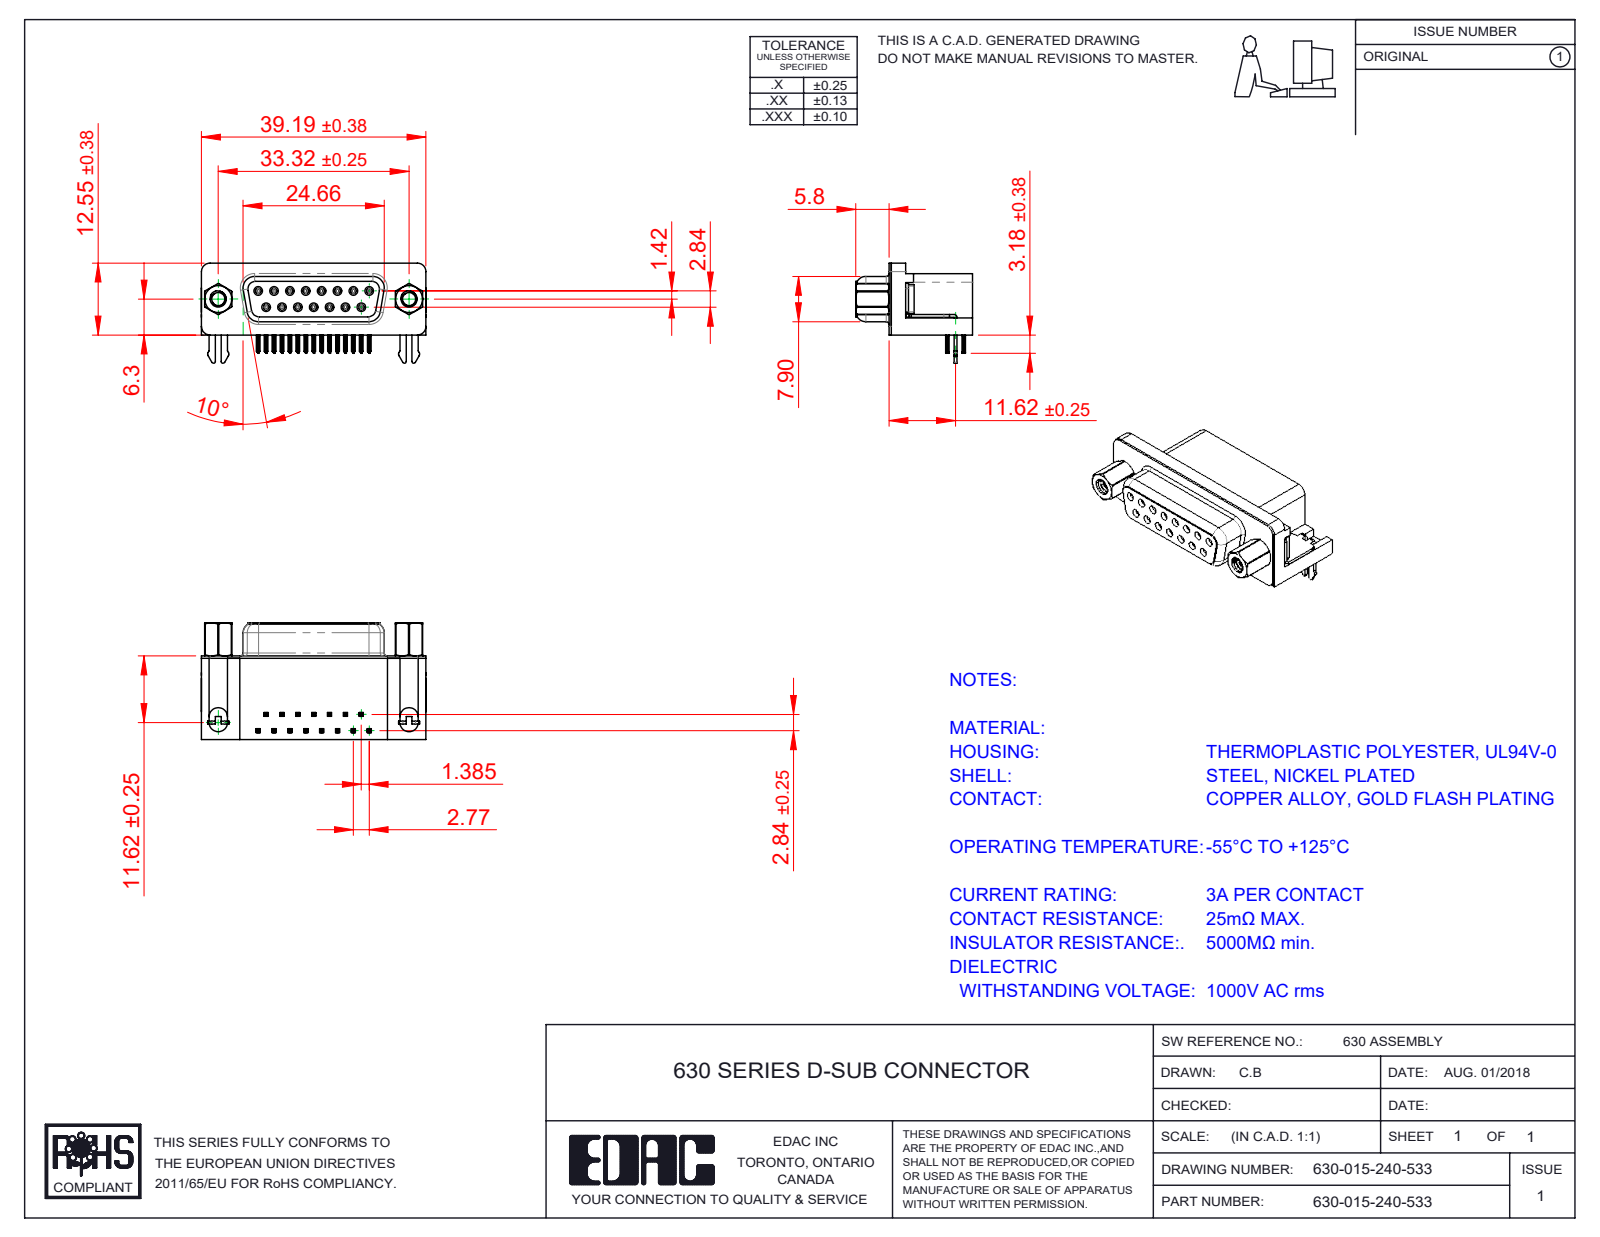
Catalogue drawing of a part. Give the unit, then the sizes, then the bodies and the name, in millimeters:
Units: millimetres
Overall size (bounding box): 39.22 × 20.4 × 17.48
Round holes (diameter × count): ⌀0.8 ×15, ⌀0.9 ×15, ⌀2.26 ×2, ⌀2.29 ×2, ⌀4 ×2, ⌀4.8 ×2, ⌀5 ×2
Round bosses / shafts (diameter × count): ⌀1.2 ×15, ⌀4.9 ×2, ⌀4.75 ×2, ⌀3.9 ×2, ⌀2.79 ×2
Partial cylindrical surfaces — rounded edges, fillets, slot ends (radius × count): R0.1 ×120, R0.15 ×60, R0.35 ×30, R1 ×18, R0.34 ×15, R0.5 ×10, R0.25 ×8, R1.35 ×8
Main face-to-face distances: 0.4, 6.2, 2.73, 14.2, 10.35, 14.6, 2.9, 3.18, 5.8, 6.65
Hole centre spacings: 3.16, 2.77, 5.54, 5.03, 5.04, 7.48, 7.49, 8.31
Volume: 6 073 mm³ · Surface area: 7 688 mm²
Bodies: 23 solids, 2591 faces (1126 planar, 685 cylindrical, 780 other)
Part name (STEP PRODUCT): 630 Shell_15 Socket; 630 Contact Bottom; 630 4-40 Hex Standoff 5; 630 4-40 Threaded Rivet (+4 more)
STEP written by: SolidWorks 2020 (CONFIG_CONTROL_DESIGN)
